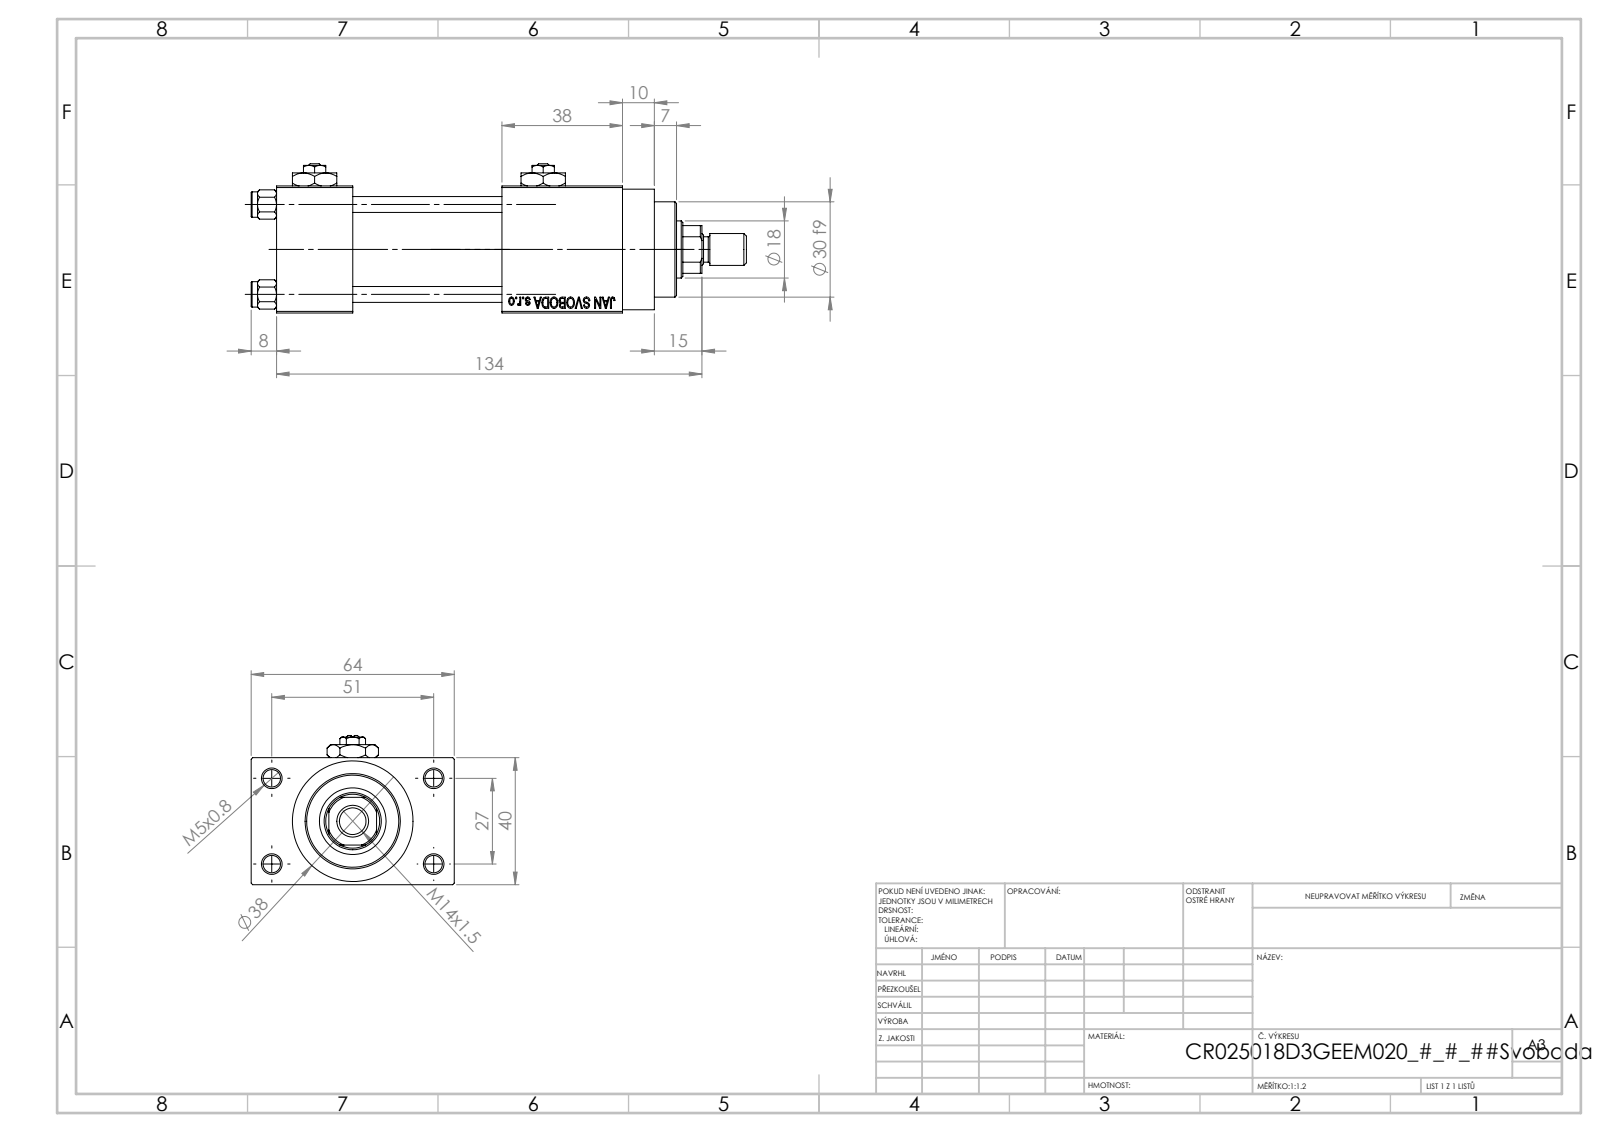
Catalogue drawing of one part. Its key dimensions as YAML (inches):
part_name: "V215CR_VCP_D; V215_VC_A; V215CR_D_TYCINKA; ROD_END_E (+3 more)"
step_written_by: "SolidWorks 2019 (CONFIG_CONTROL_DESIGN)"
units: inches
bodies: {solids: 14, faces: 1213, planar: 545, cylindrical: 102, other: 566}
overall_size: [6.142, 2.52, 1.85]
volume: 11.03
surface_area: 103
round_holes:
  - {diameter: 0.197, count: 4}
  - {diameter: 0.217, count: 4}
  - {diameter: 0.787, count: 3}
  - {diameter: 0.276, count: 2}
  - {diameter: 0.518, count: 2}
  - {diameter: 0.335, count: 1}
  - {diameter: 0.709, count: 1}
  - {diameter: 0.827, count: 1}
  - {diameter: 0.984, count: 1}
  - {diameter: 1.181, count: 1}
round_bosses_or_shafts:
  - {diameter: 0.315, count: 5}
  - {diameter: 1.496, count: 1}
  - {diameter: 1.22, count: 1}
  - {diameter: 0.394, count: 1}
partial_cylinders:
  - {radius: 0.335, count: 1}
face_to_face_distances: [1.575, 2.047, 0.472, 1.85, 2.795, 0.945, 2.52, 1.496, 3.346, 4.291]
hole_center_spacings: [0.448, 0.788, 1.114, 1.136, 1.177, 1.561, 1.903, 1.063]
